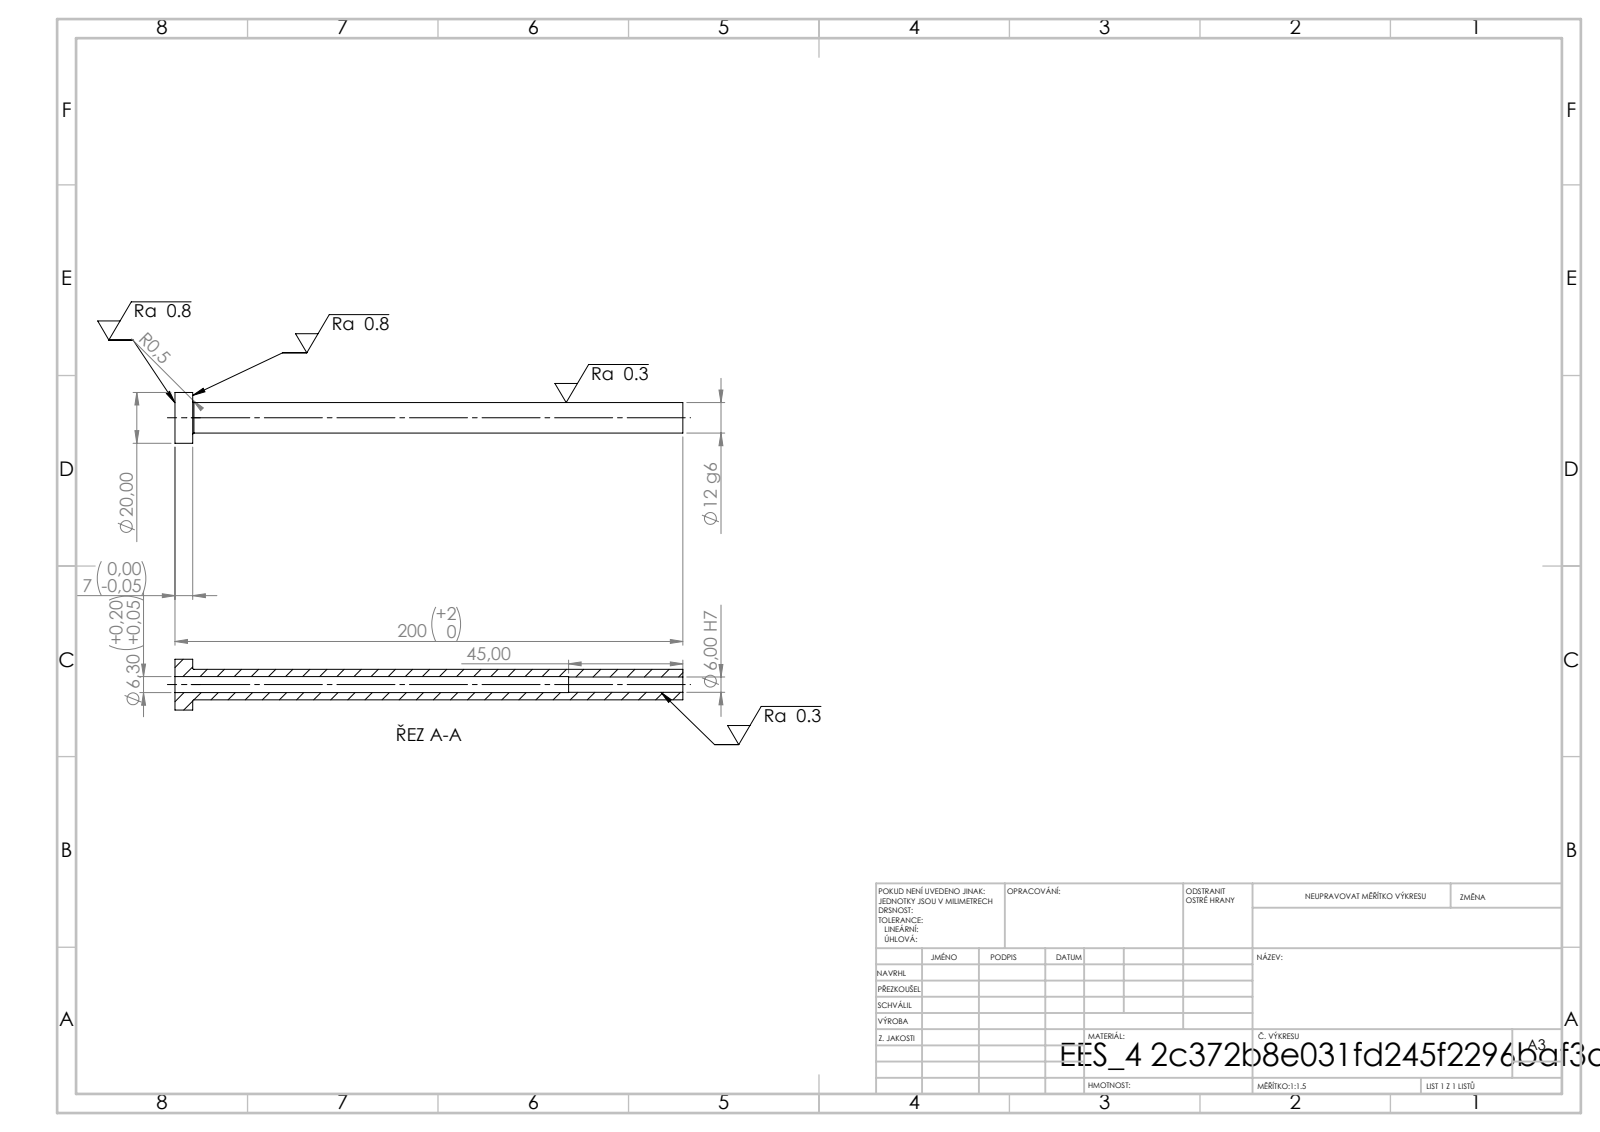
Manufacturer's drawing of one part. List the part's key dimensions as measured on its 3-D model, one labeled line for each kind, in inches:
STEP written by: SolidWorks 2019 (CONFIG_CONTROL_DESIGN)
Units: inches
Bodies: 1 solid, 14 faces (4 planar, 8 cylindrical, 2 other)
Overall size (bounding box): 7.874 × 0.787 × 0.787
Volume: 1.094 in³ · Surface area: 18.9 in²
Round holes (diameter × count): ⌀0.236 ×1, ⌀0.248 ×1
Round bosses / shafts (diameter × count): ⌀0.787 ×1, ⌀0.472 ×1
Main face-to-face distances: 0.276, 7.874, 7.598, 6.102, 5.827, 1.772
